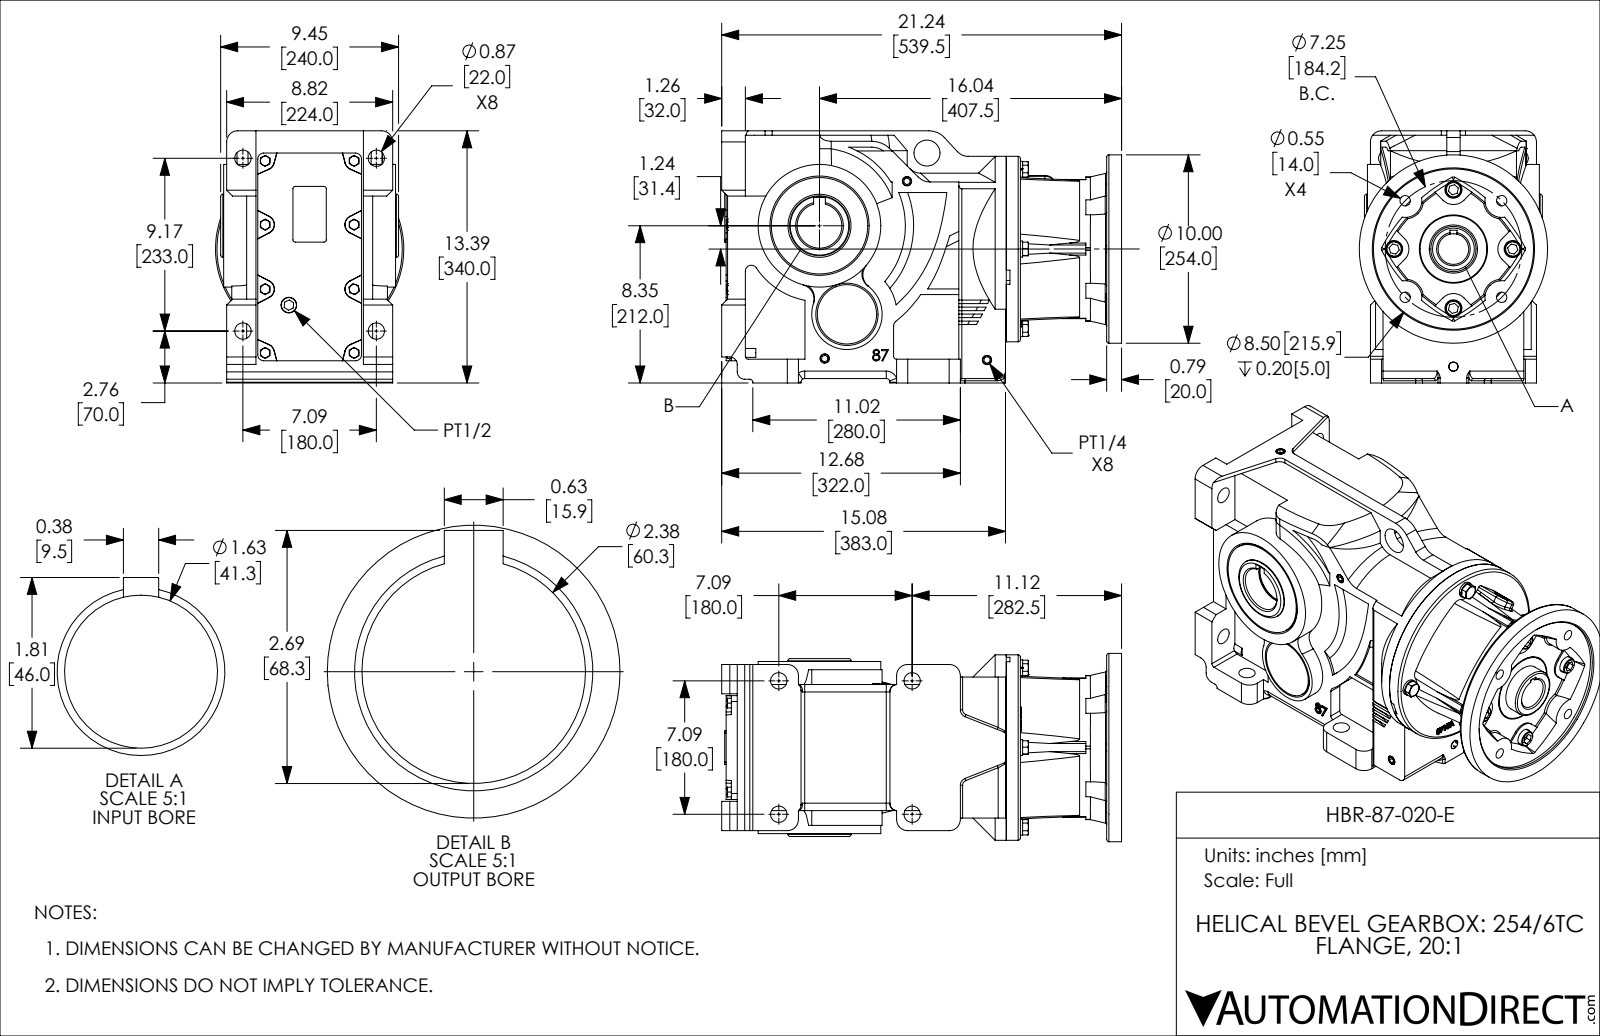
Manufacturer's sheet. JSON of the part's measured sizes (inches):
{"part_name": "HBR-87-020-E", "step_written_by": "SolidWorks 2018 (AUTOMOTIVE_DESIGN)", "units": "inches", "bodies": {"solids": 9, "faces": 1202, "planar": 588, "cylindrical": 312, "other": 302}, "overall_size": [21.24, 13.501, 10], "volume_in3": 1541, "surface_area_in2": 1576, "round_holes": [[0.551, 8], [0.866, 8], [0.48, 4], [0.496, 4], [0.906, 4], [0.473, 1], [0.709, 1], [0.827, 1], [1.125, 1], [1.378, 1], [1.417, 1], [1.625, 1]], "round_bosses_or_shafts": [[0.827, 5], [0.846, 4], [0.472, 4], [10, 1], [9.843, 1], [6.513, 1], [5.118, 1], [3.543, 1]], "partial_cylinders_radius": [[0.118, 20], [0.394, 15], [0.591, 14], [0.157, 11], [0.315, 6], [0.787, 5], [0.008, 4], [0.748, 4]], "face_to_face_distances": [0.669, 0.236, 6.024, 1.024, 0.787, 1.063, 7.087, 13.15, 20.217, 0.394], "hole_center_spacings": [5.276, 2.63, 7.087, 7.263, 1.083, 3.059, 3.15, 4.232]}
